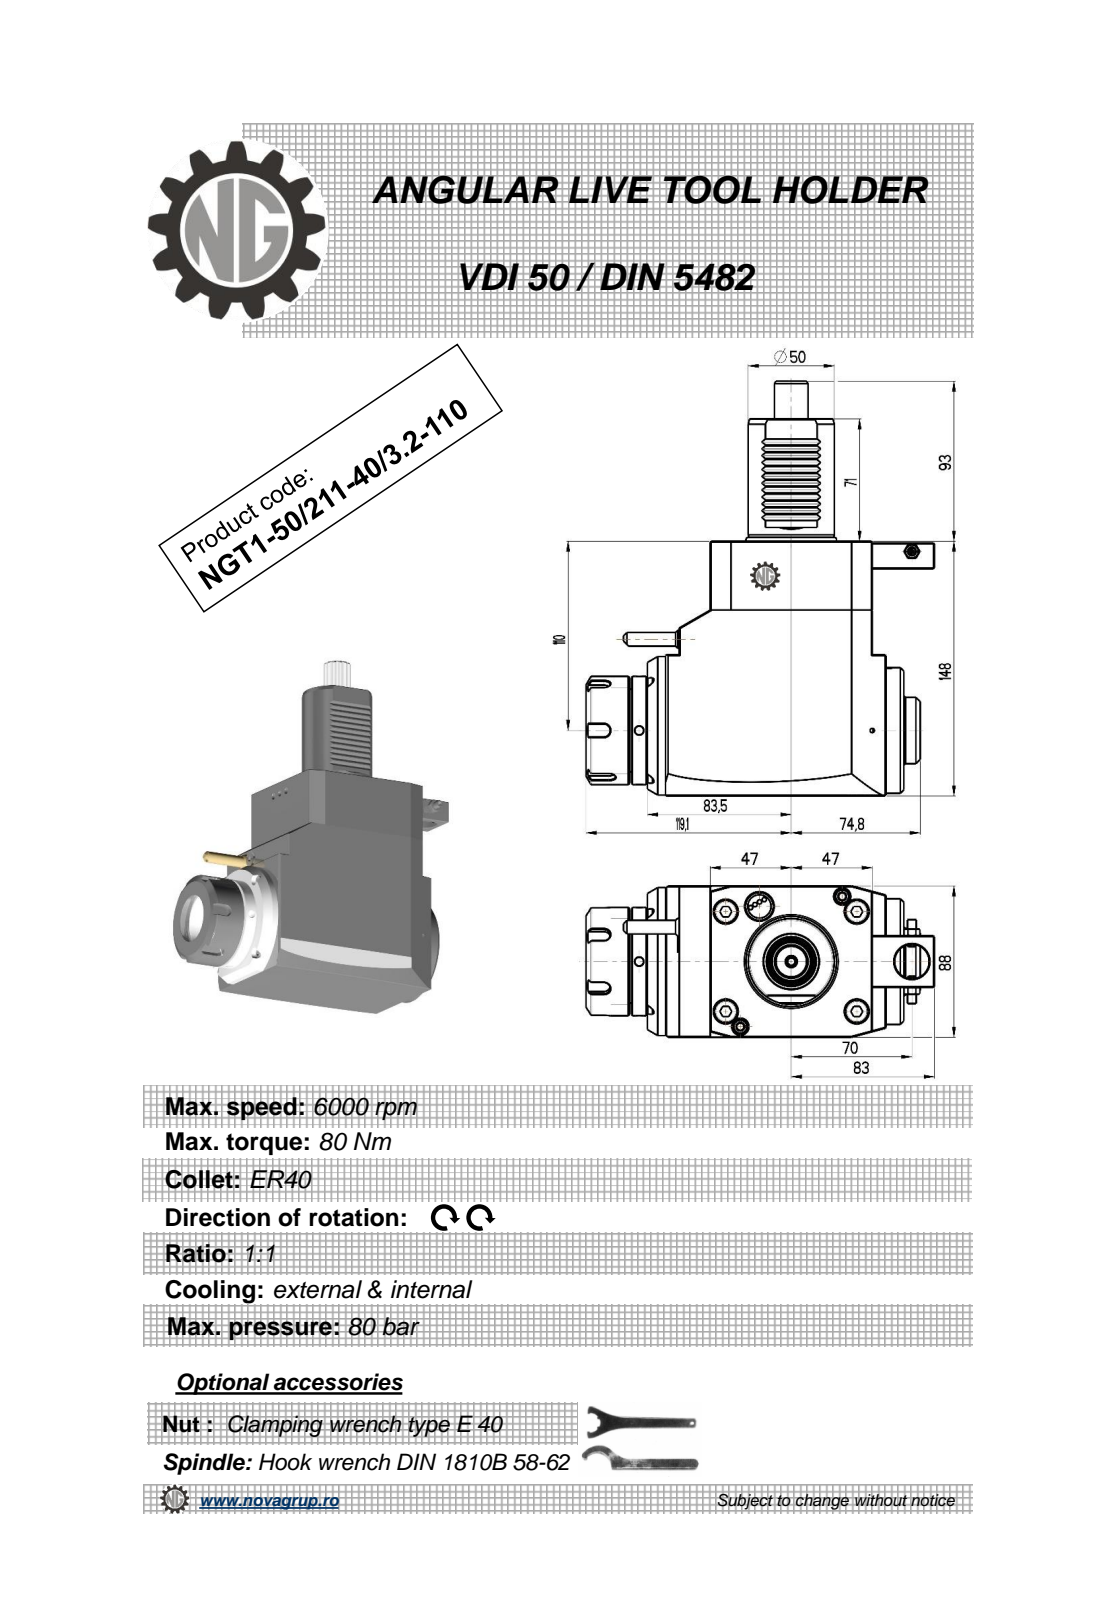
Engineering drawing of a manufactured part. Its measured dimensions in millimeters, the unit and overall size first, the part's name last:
Units: millimetres
Overall size (bounding box): 241 × 202.1 × 88
Round holes (diameter × count): ⌀5 ×3, ⌀3 ×1, ⌀4.2 ×1, ⌀4.5 ×1, ⌀5.3 ×1, ⌀9.5 ×1, ⌀20 ×1, ⌀33.5 ×1
Round bosses / shafts (diameter × count): ⌀86 ×1, ⌀73 ×1, ⌀63 ×1, ⌀51 ×1, ⌀50 ×1, ⌀40 ×1, ⌀38.5 ×1, ⌀10 ×1
Partial cylindrical surfaces — rounded edges, fillets, slot ends (radius × count): R3.33 ×24, R0.26 ×12, R0.3 ×12, R0.2 ×6, R3.75 ×5, R8.25 ×1, R9.75 ×1
Main face-to-face distances: 88, 148, 8, 94, 36.5, 130.5, 120, 148.8, 112.3, 18.3
Hole centre spacings: 52.46, 56.65, 70, 88.25, 101.5, 158.25
Volume: 1 845 000 mm³ · Surface area: 116 341 mm²
Bodies: 1 solid, 496 faces (203 planar, 148 cylindrical, 145 other)
Part name (STEP PRODUCT): NGT1_50_211_40_3_2_110
STEP written by: PRO/ENGINEER BY PARAMETRIC TECHNOLOGY CORPORATION, 2010280 (CONFIG_CONTROL_DESIGN)
